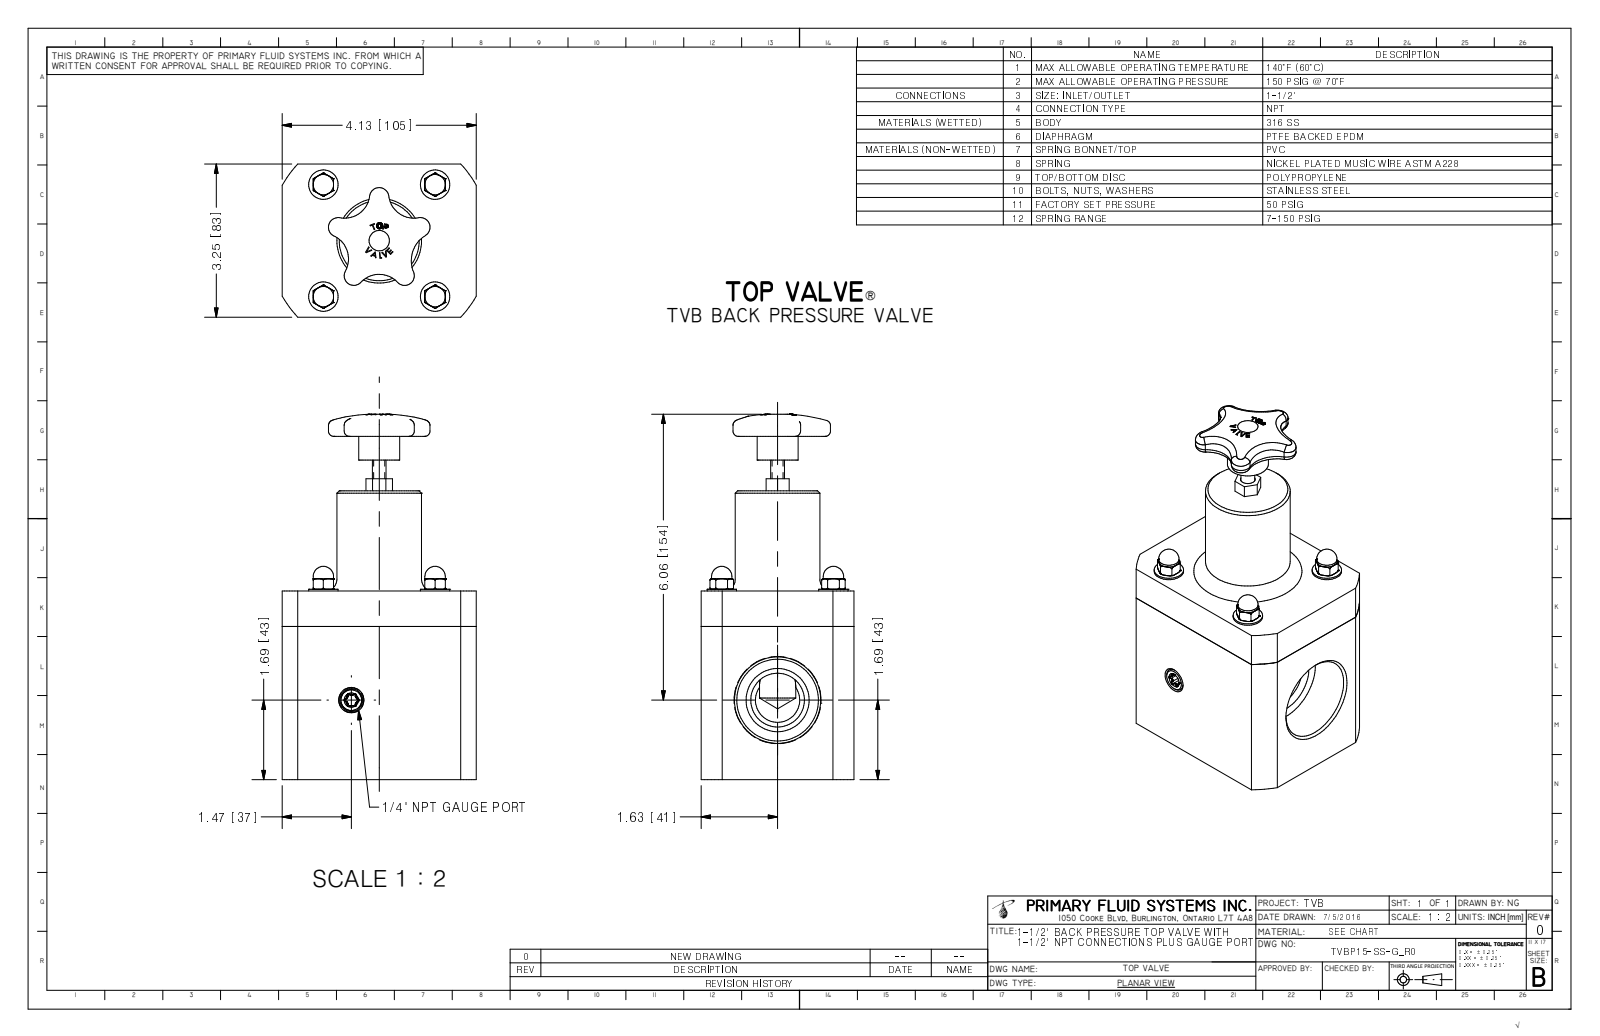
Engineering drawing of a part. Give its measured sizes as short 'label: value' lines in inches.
name: TVBP15-SS-G-R0
written by: Autodesk Inventor 2009 (AUTOMOTIVE_DESIGN)
unit: in
bodies: 1 solid, 359 faces (152 planar, 51 cylindrical, 156 other)
size: 7.752 × 4.125 × 3.25
volume: 55.2 in³; area: 119 in²
holes: 4× ⌀0.175, 1× ⌀1.734
bosses: 4× ⌀0.625, 4× ⌀0.433, 4× ⌀0.375, 1× ⌀1.8, 1× ⌀0.87, 1× ⌀0.293
rounds: 6× R0.027, 5× R0.085, 5× R0.205, 4× R0.536, 4× R0.656, 1× R0.625, 1× R0.745, 1× R2.375
face distances: 3.25, 4, 4.125, 0.9, 3.225, 2.325, 6.125, 2.125, 0.433, 4.036
hole spacings: 2.375, 2.375, 3.359
